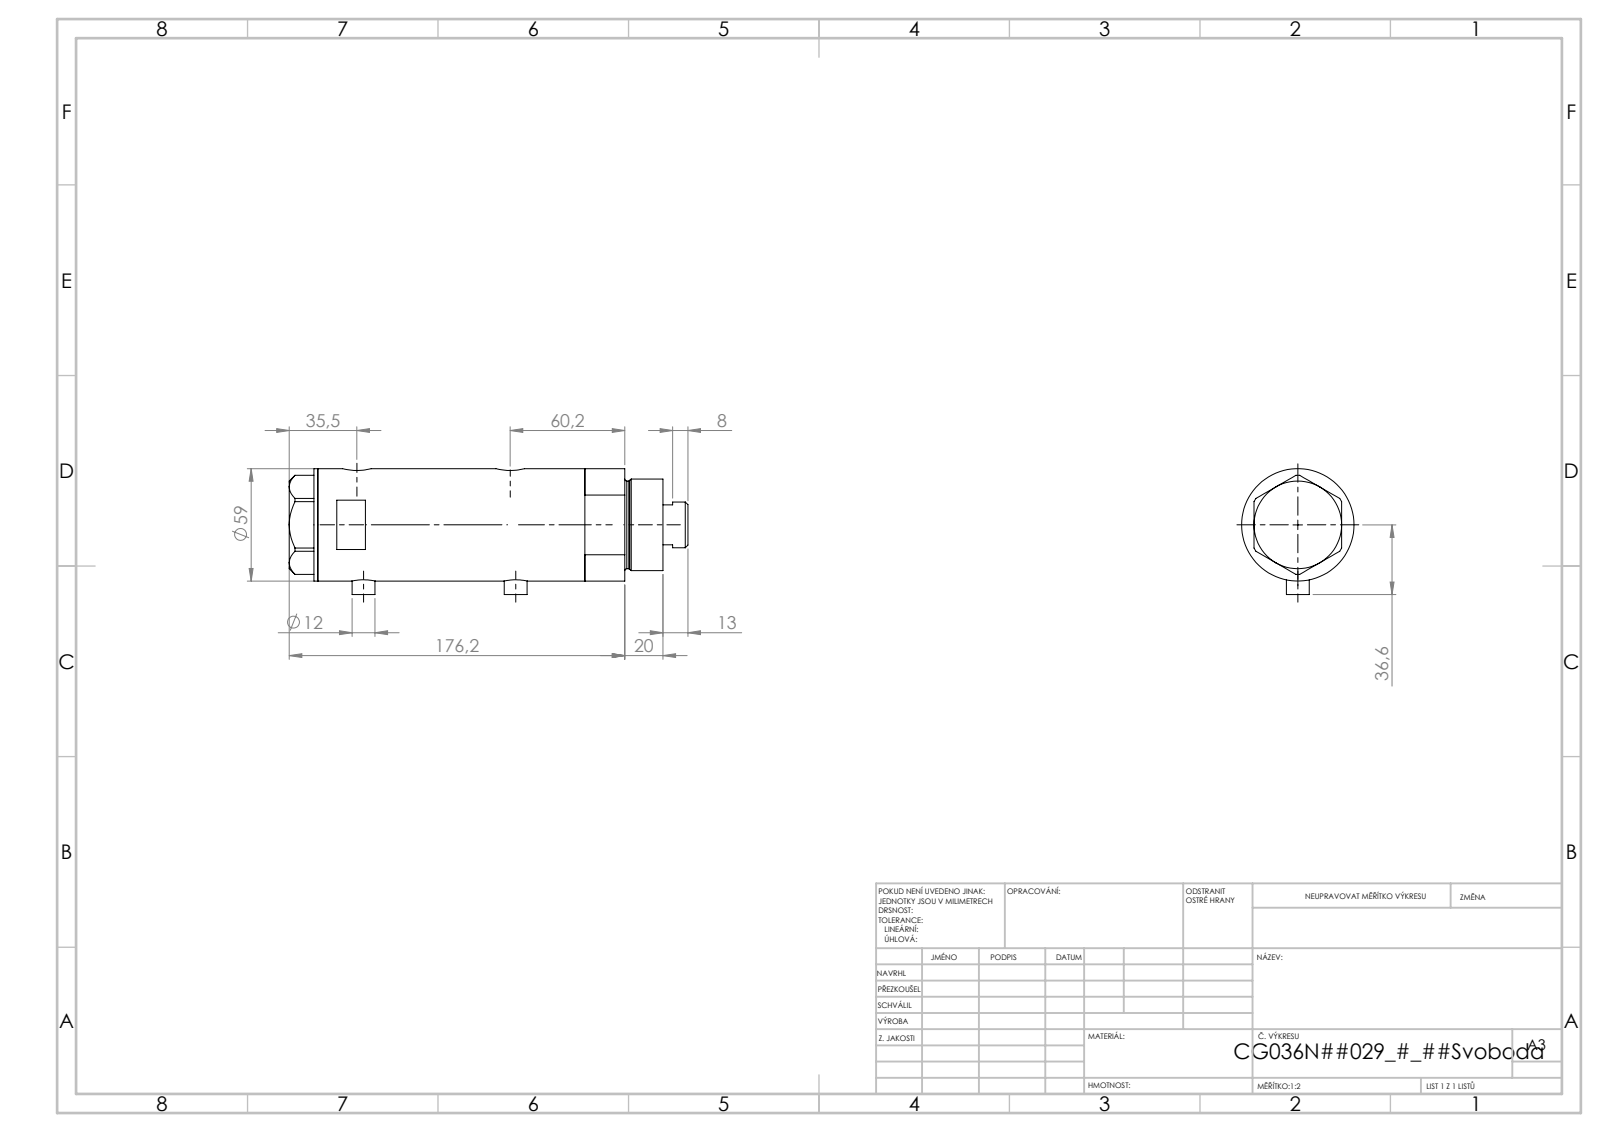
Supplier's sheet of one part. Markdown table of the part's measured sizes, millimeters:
| quantity | value |
| --- | --- |
| part name | V270CG_VC; V270CG_MIDDLE; V270CG_FRONT; V270CG_BACK |
| STEP written by | SolidWorks 2019 (CONFIG_CONTROL_DESIGN) |
| units | millimeters |
| bodies | 4 solids, 126 faces (53 planar, 53 cylindrical, 20 other) |
| overall size | 209.3 × 66.1 × 59 |
| volume | 487 000 mm³ |
| surface area | 100 848 mm² |
| round holes (diameter × count) | 5 × 2, 9.73 × 2, 12.5 × 2, 15 × 2, 8.5 × 1, 25 × 1, 26.5 × 1, 36 × 1, 40 × 1, 52 × 1 |
| round bosses / shafts (diameter × count) | 12 × 2, 59 × 1, 48 × 1, 46 × 1, 24 × 1 |
| main face-to-face distances | 102.2, 23.5, 78.7, 15, 38.5, 117.2, 2, 181.2, 196.2, 157.7 |
| hole center spacings | 2.9, 3.5, 77, 79.9, 80.5, 83.4 |
